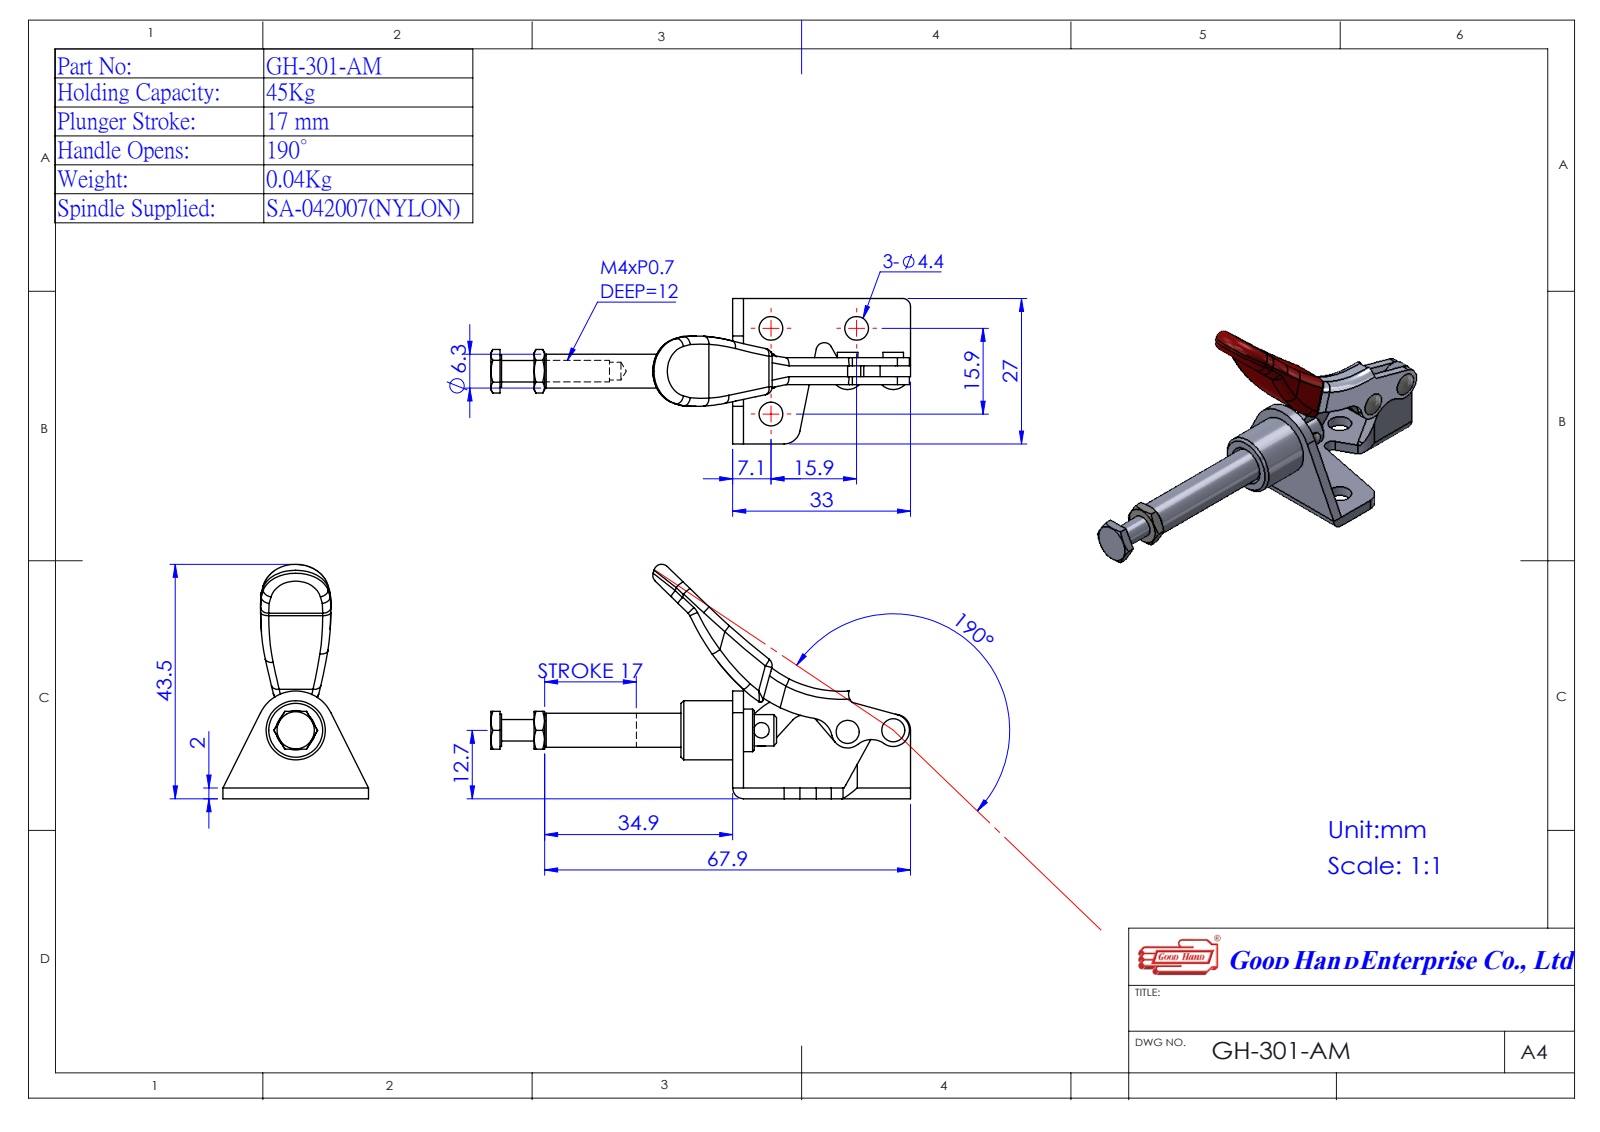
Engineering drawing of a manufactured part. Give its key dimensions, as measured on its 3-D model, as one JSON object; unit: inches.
{"part_name": "Group2^493788(GH-301-AM); 493788(GH-301-AM); Group1^493788(GH-301-AM); 1301AM05-1^493788(GH-301-AM) (+1 more)", "step_written_by": "SolidWorks 2016 (AUTOMOTIVE_DESIGN)", "units": "inches", "bodies": {"solids": 6, "faces": 168, "planar": 64, "cylindrical": 83, "other": 21}, "overall_size": [3.107, 1.835, 1.063], "volume_in3": 0.398, "surface_area_in2": 10.2, "round_holes": [[0.173, 3], [0.098, 2]], "round_bosses_or_shafts": [[0.15, 3], [0.433, 1], [0.311, 1], [0.236, 1], [0.157, 1], [0.098, 1]], "partial_cylinders_radius": [[0.118, 6], [0.059, 2], [0.157, 2], [1.462, 2], [0.055, 1], [0.079, 1], [0.13, 1], [0.242, 1]], "face_to_face_distances": [0.079, 0.059, 0.138, 0.197, 0.433, 0.492, 0.571, 0.63, 0.276, 0.484], "hole_center_spacings": [0.626, 0.334, 0.885]}
